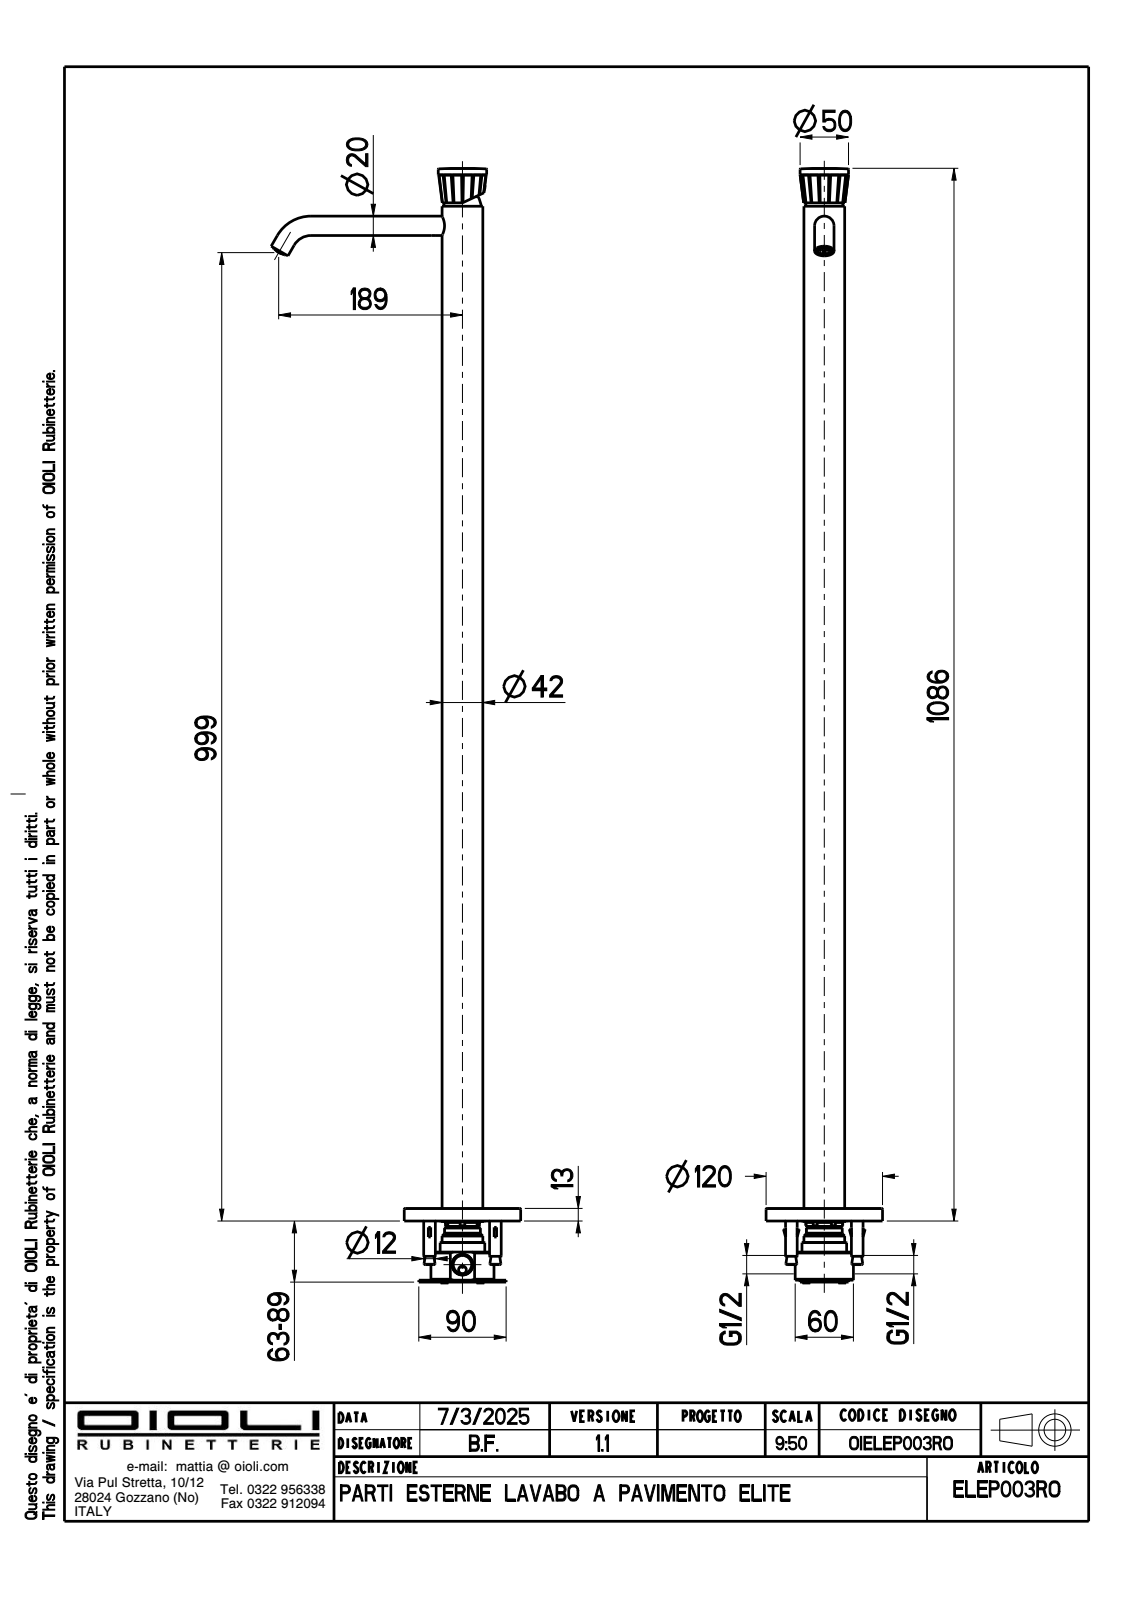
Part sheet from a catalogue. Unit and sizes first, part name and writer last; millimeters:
Units: millimetres
Overall size (bounding box): 1085.62 × 257.13 × 120
Round holes (diameter × count): ⌀15.5 ×2, ⌀3.3 ×1, ⌀4 ×1, ⌀4.2 ×1, ⌀5.3 ×1, ⌀6.5 ×1, ⌀10 ×1, ⌀14.5 ×1, ⌀14.55 ×1, ⌀15 ×1, ⌀16.5 ×1, ⌀16.75 ×1
Round bosses / shafts (diameter × count): ⌀20 ×2, ⌀16.5 ×2, ⌀120 ×1, ⌀60 ×1, ⌀49.9 ×1, ⌀42 ×1, ⌀40 ×1, ⌀33 ×1
Partial cylindrical surfaces — rounded edges, fillets, slot ends (radius × count): R0.1 ×14, R0.9 ×8, R0.6 ×6, R0.45 ×3, R2.5 ×1, R6.72 ×1, R7.46 ×1, R9 ×1
Main face-to-face distances: 2, 5, 3, 1074.5, 1071.5, 1069.5, 8, 13, 11, 1082.5
Hole centre spacings: 29.97, 40.5
Volume: 396 878 mm³ · Surface area: 329 345 mm²
Bodies: 9 solids, 903 faces (560 planar, 151 cylindrical, 192 other)
Part name (STEP PRODUCT): OIBR00629; OIBR00327; OICT00021; OIAR00046 (+5 more)
STEP written by: CREO PARAMETRIC BY PTC INC, 2024493 (CONFIG_CONTROL_DESIGN)
